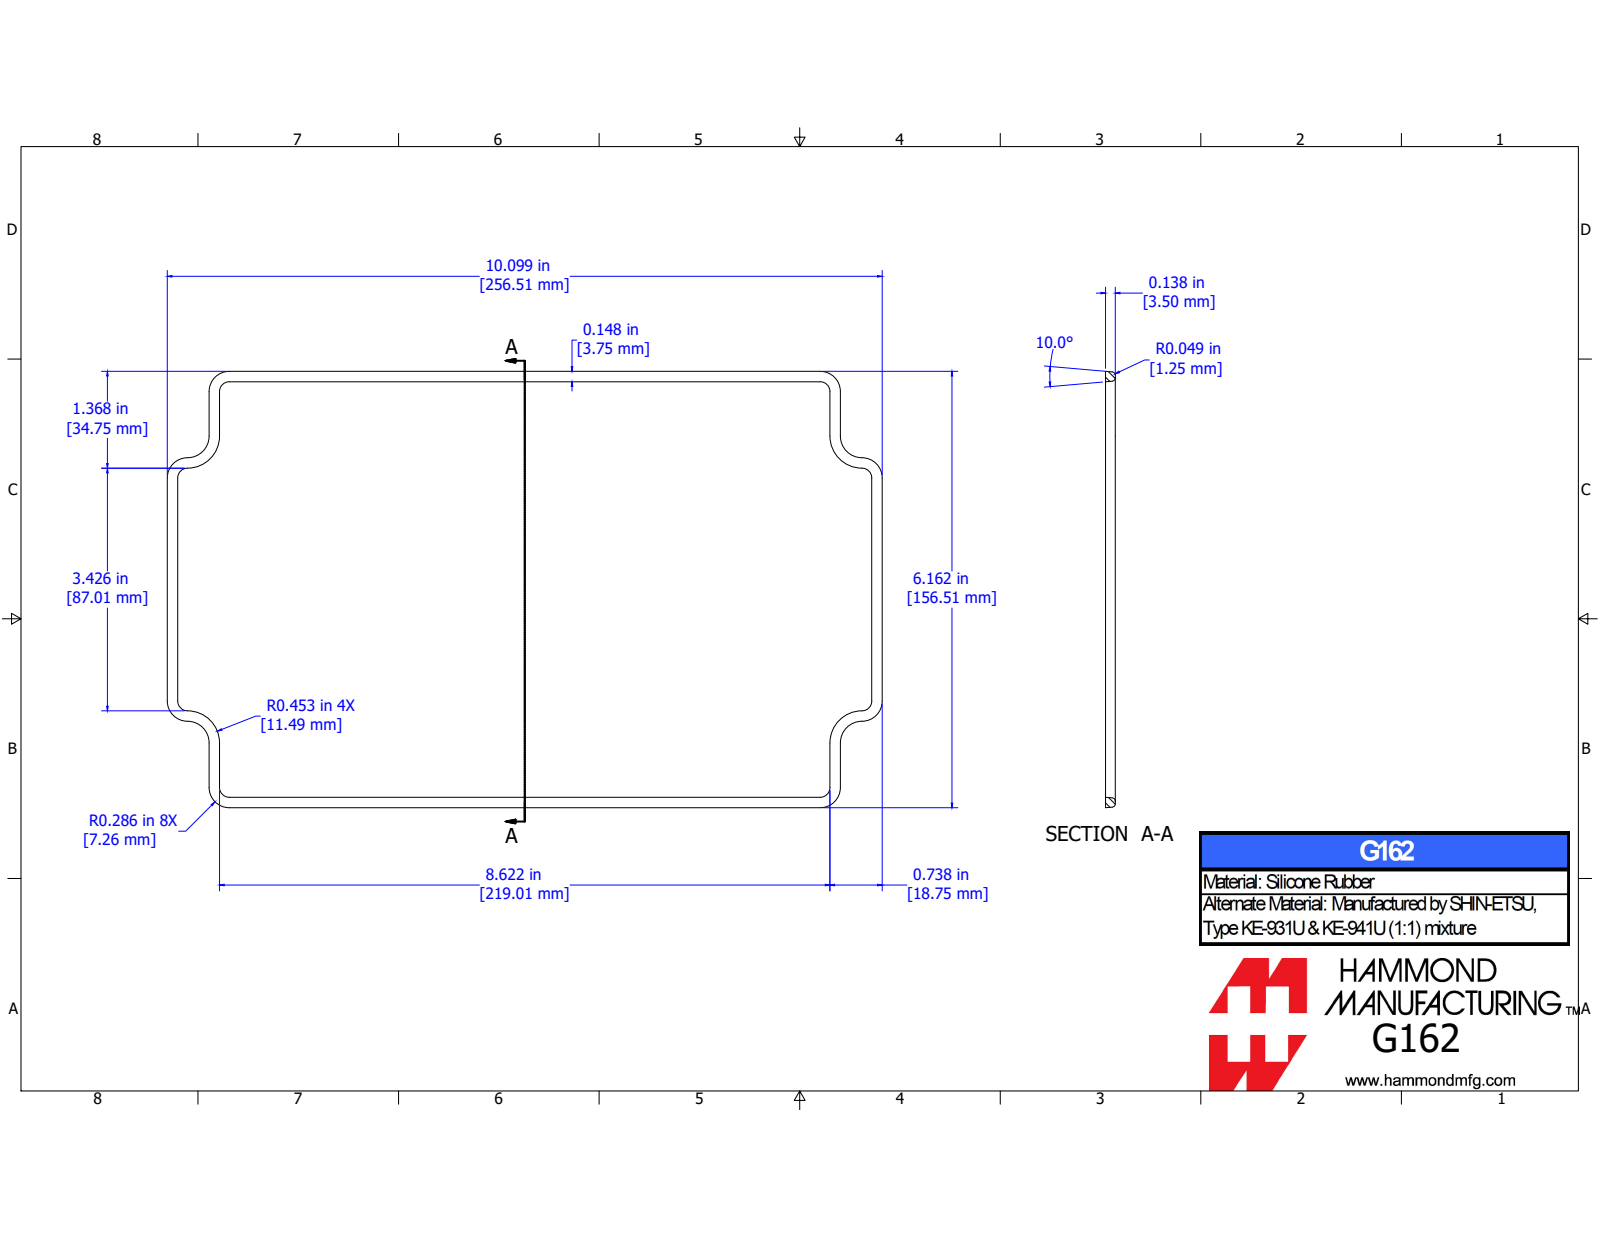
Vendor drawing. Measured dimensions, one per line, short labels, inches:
name: 1590Z162G
written by: SolidWorks 2019 (CONFIG_CONTROL_DESIGN)
unit: in
bodies: 1 solid, 82 faces (18 planar, 16 cylindrical, 48 other)
size: 10.093 × 6.156 × 0.138
volume: 0.509 in³; area: 15.11 in²
rounds: 12× R0.039
face distances: 6.027, 0.138, 9.964, 0.61, 9.354, 8.744
